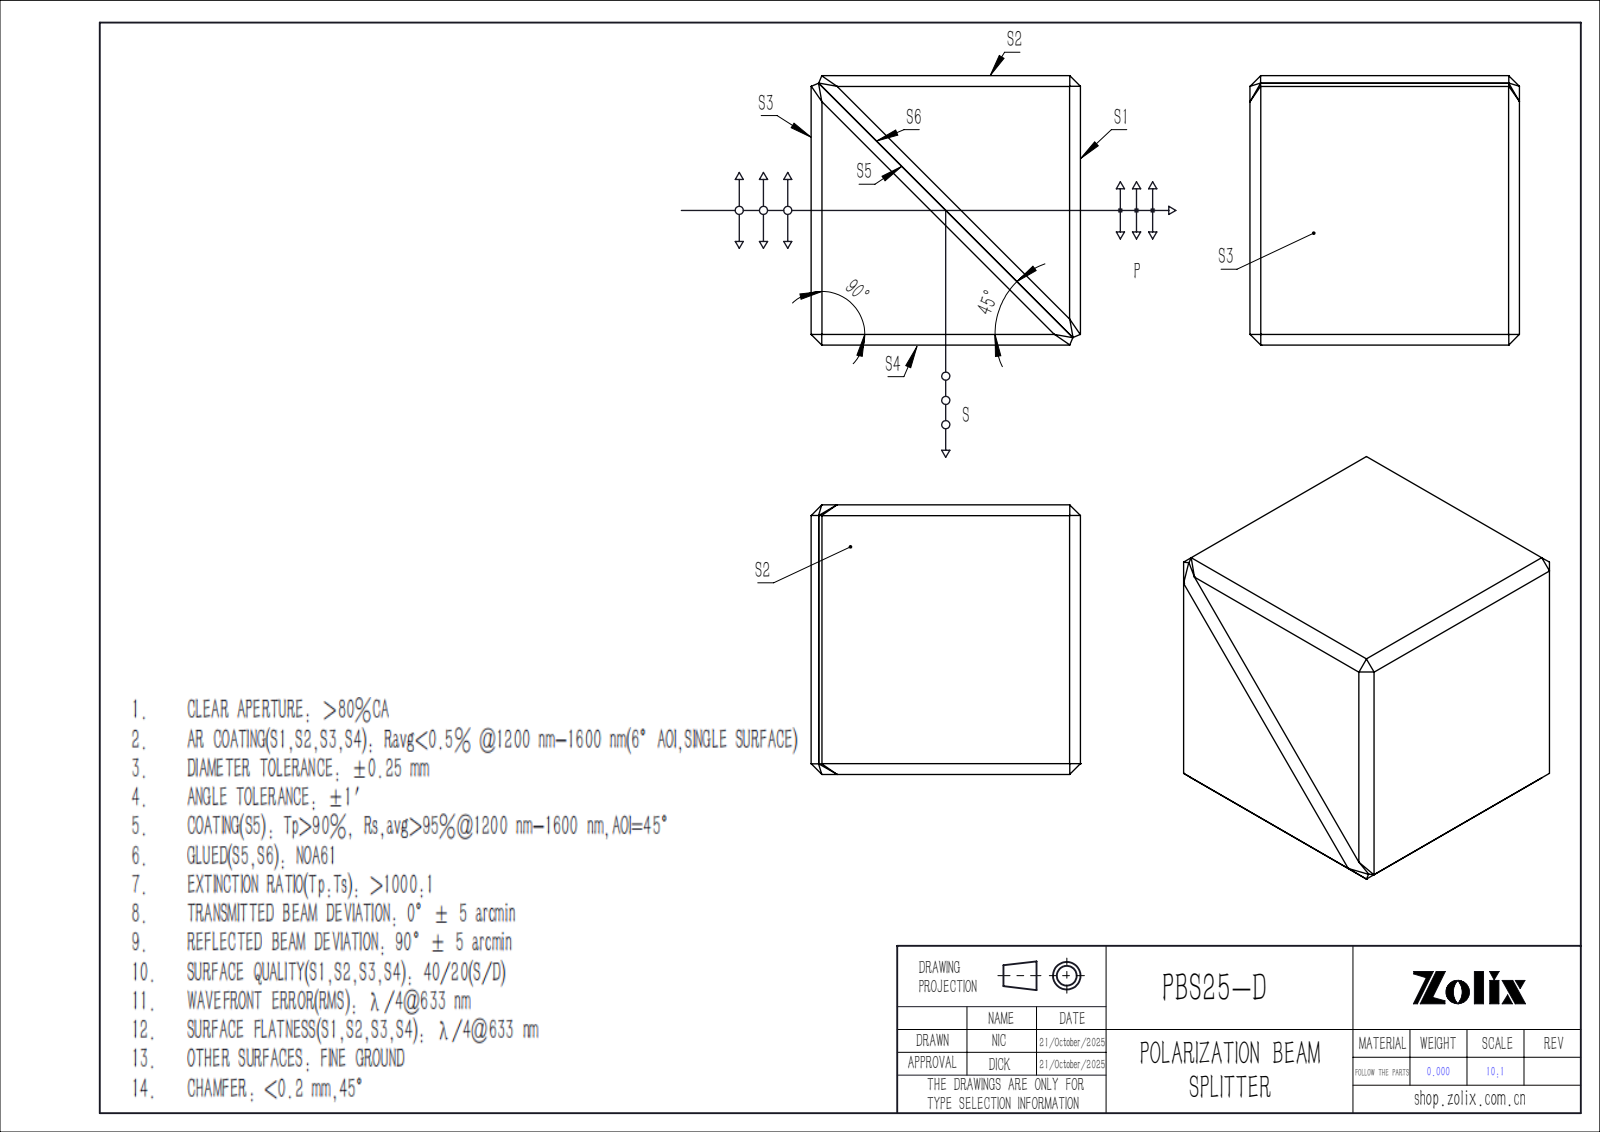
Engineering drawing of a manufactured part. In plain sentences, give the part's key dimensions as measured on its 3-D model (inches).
The part is named "PBS644; PBS644-1-2; PBS644-1-1". Its 3-D file was written by "SolidWorks 2022 (CONFIG_CONTROL_DESIGN)". It is 2 solids with 43 faces: 41 planar, 2 cylindrical and 0 other. Overall it measures 1 by 1 by 1 inches. Its volume is 0.999 cubic inches and its surface area 8.717 square inches. Round holes: 1 of diameter 0.02. The main face-to-face distances are 1, 1.403, 0.696, 1.403, 1.293, 0.701, 0.702, 1.713, 1.501, 1.502.
